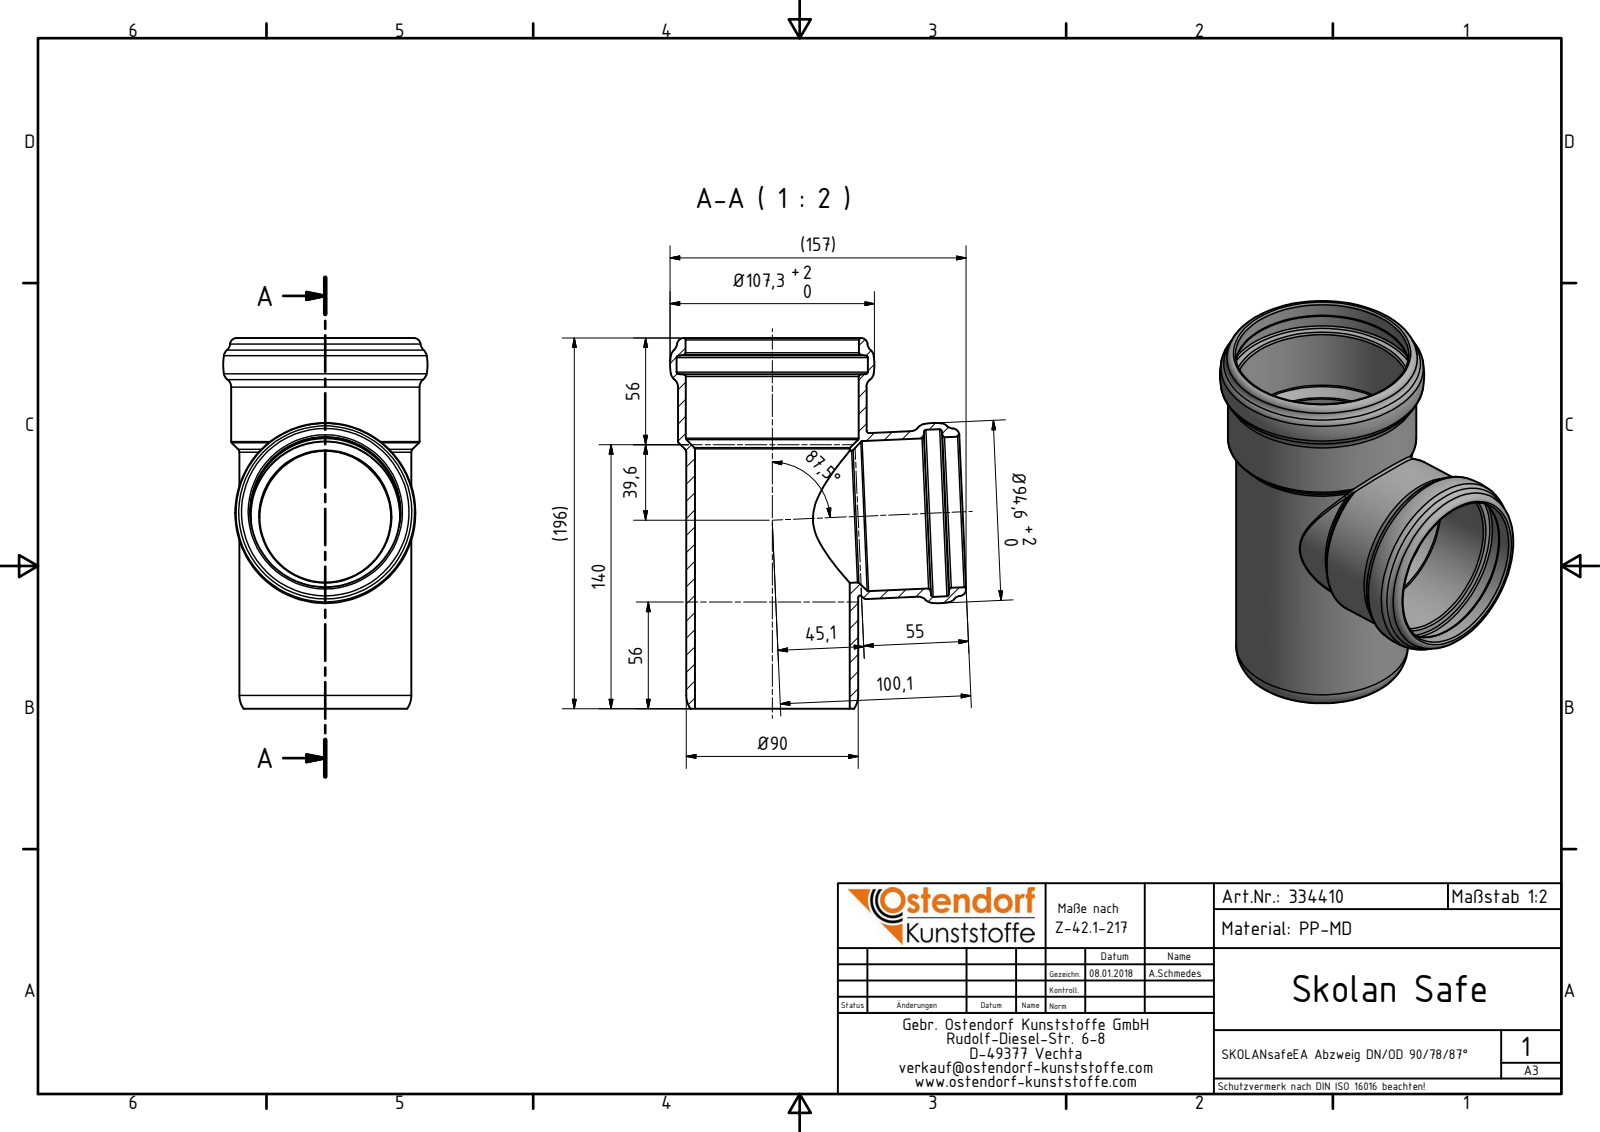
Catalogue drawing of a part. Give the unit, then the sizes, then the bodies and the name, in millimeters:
Units: millimetres
Overall size (bounding box): 194.6 × 155.43 × 107.3
Round holes (diameter × count): ⌀69.2 ×1, ⌀78.8 ×1, ⌀79 ×1, ⌀81.3 ×1, ⌀87.8 ×1, ⌀90.8 ×1, ⌀91.1 ×1, ⌀100.5 ×1
Round bosses / shafts (diameter × count): ⌀99 ×1, ⌀90.3 ×1, ⌀87 ×1
Partial cylindrical surfaces — rounded edges, fillets, slot ends (radius × count): R39.1 ×1
Volume: 295 804 mm³ · Surface area: 142 190 mm²
Bodies: 1 solid, 62 faces (1 planar, 13 cylindrical, 48 other)
Part name (STEP PRODUCT): 334410 SKOLANsafeEA Abzweiger DN_OD 90_78_87°
STEP written by: Autodesk Inventor 2016 (AUTOMOTIVE_DESIGN)
